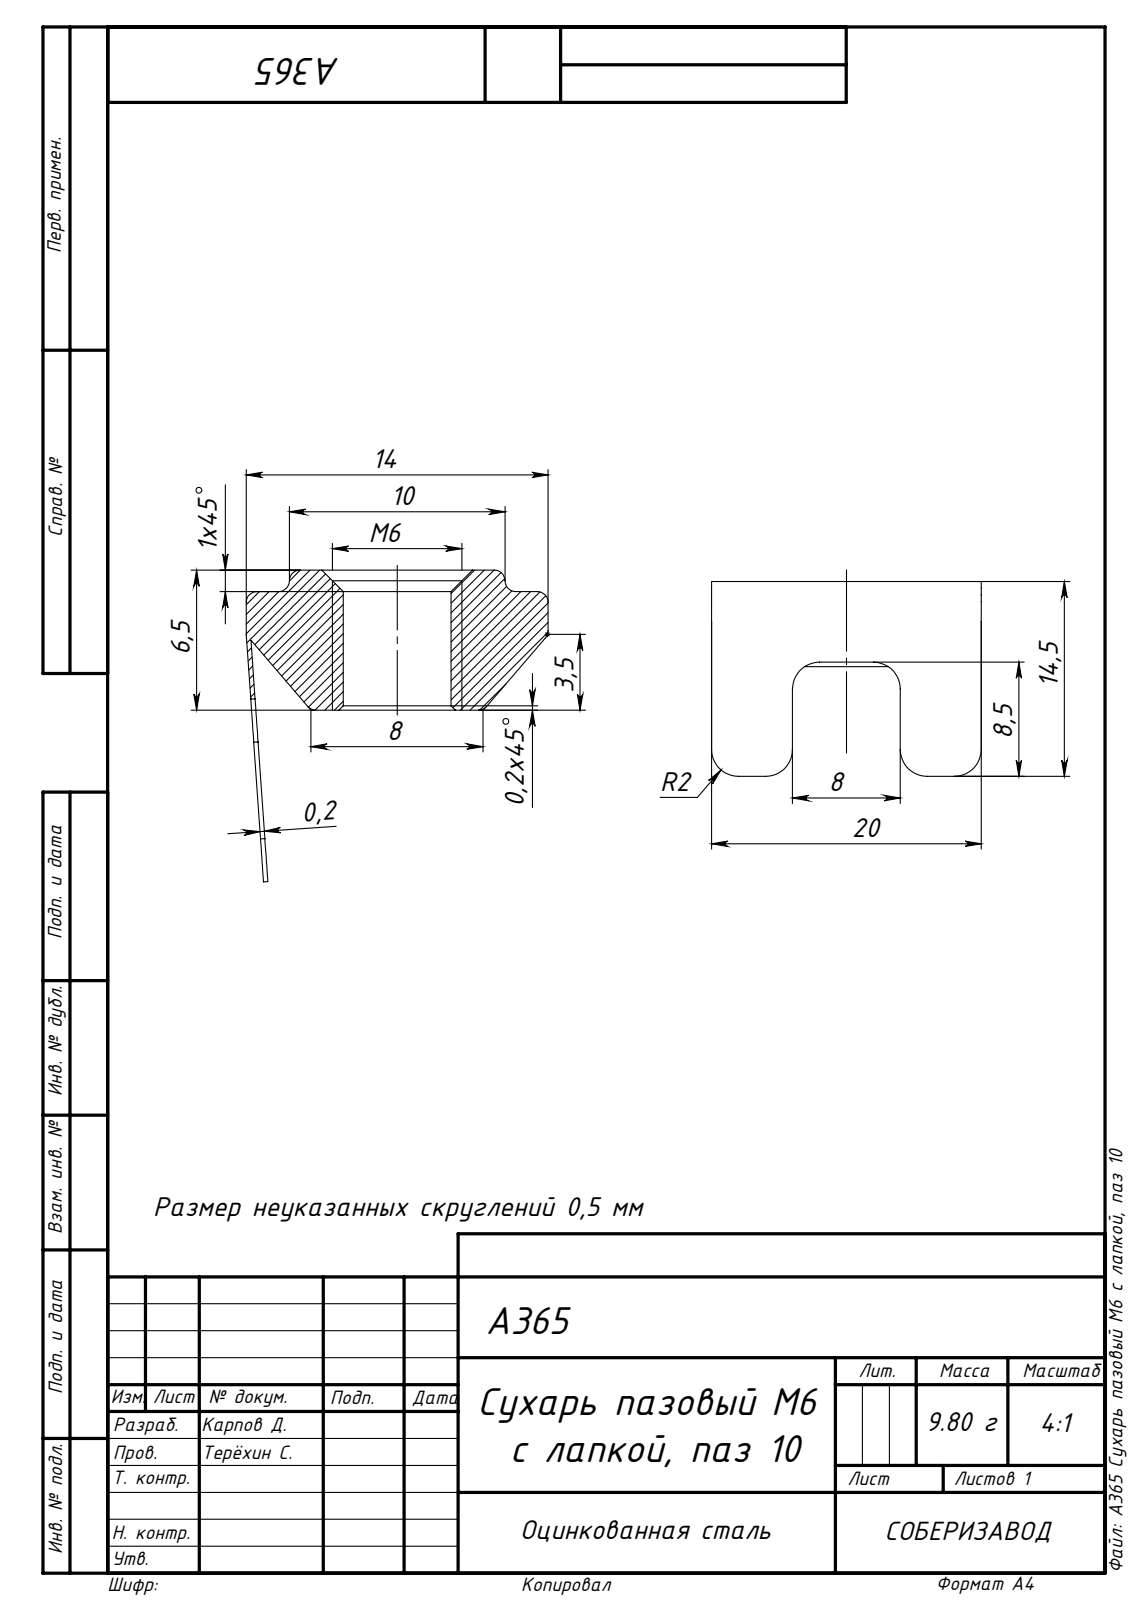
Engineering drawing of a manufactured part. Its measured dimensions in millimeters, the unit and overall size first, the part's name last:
Units: millimetres
Overall size (bounding box): 20 × 14.07 × 14
Round holes (diameter × count): ⌀5 ×1
Partial cylindrical surfaces — rounded edges, fillets, slot ends (radius × count): R0.5 ×8, R2 ×6, R0.2 ×2
Main face-to-face distances: 6.5, 20, 1, 5.5, 14, 2, 12, 10, 6, 8
Volume: 1 419 mm³ · Surface area: 1 231 mm²
Bodies: 1 solid, 41 faces (19 planar, 18 cylindrical, 4 other)
Part name (STEP PRODUCT): A365 Сухарь пазовый М6 с лапкой, паз 10
STEP written by: SolidWorks 2018 (AUTOMOTIVE_DESIGN)
